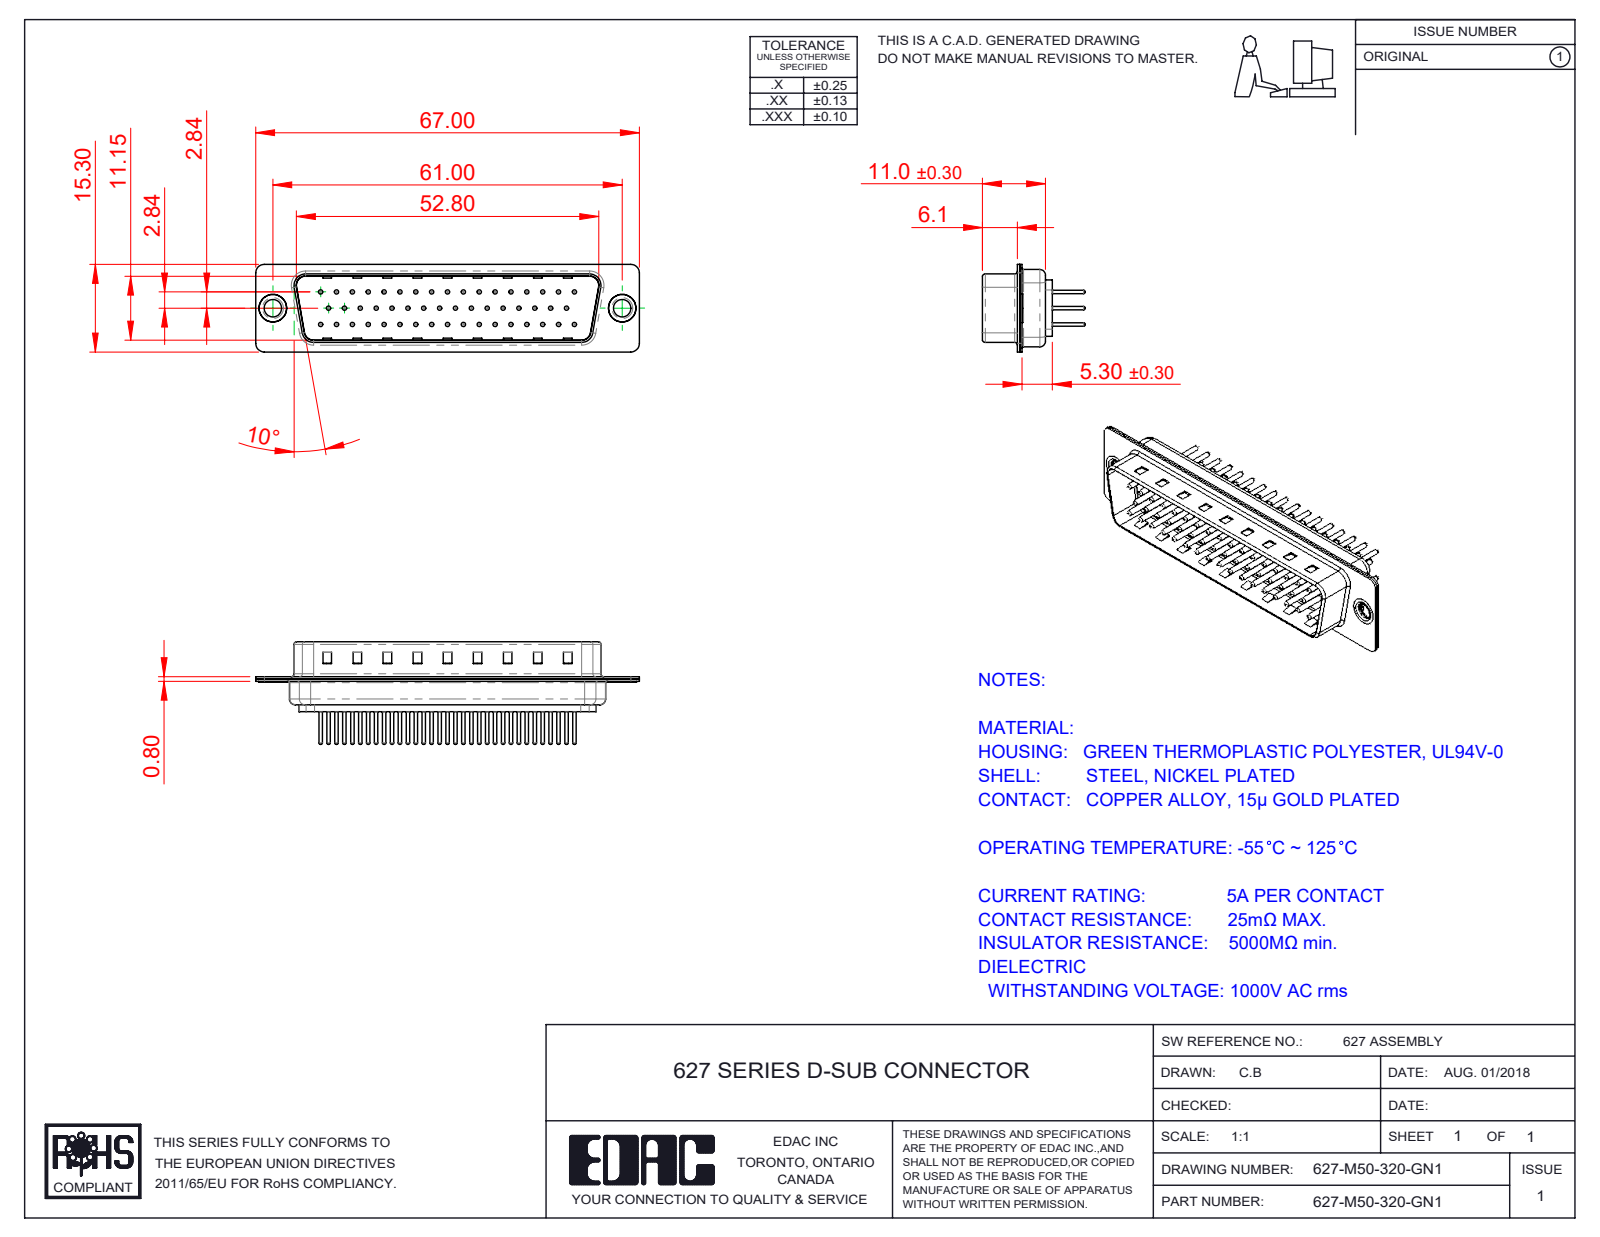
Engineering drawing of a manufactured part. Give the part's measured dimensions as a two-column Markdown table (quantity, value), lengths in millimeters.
| quantity | value |
| --- | --- |
| part name | 627M Housing_50 Contacts; 627M Contact Row 1_20; 627M Shell Rear_50 Contacts; 627M Thru Hole Rivet (+4 more) |
| STEP written by | SolidWorks 2020 (CONFIG_CONTROL_DESIGN) |
| units | millimeters |
| bodies | 55 solids, 2236 faces (553 planar, 825 cylindrical, 858 other) |
| overall size | 67 × 17.9 × 15.3 |
| volume | 4 447 mm³ |
| surface area | 10 554 mm² |
| round holes (diameter × count) | 0.75 × 50, 1.6 × 50, 2 × 50, 3.05 × 2, 4 × 2, 4.8 × 2 |
| round bosses / shafts (diameter × count) | 1.5 × 50, 0.6 × 50, 5 × 2, 4.9 × 2, 3.55 × 2 |
| partial cylindrical surfaces (radius × count) | 1.5 × 16, 2 × 12, 0.5 × 8, 1.6 × 8, 0.25 × 4, 0.6 × 4, 0.65 × 4, 0.9 × 4 |
| main face-to-face distances | 0.4, 11.55, 5.7, 6.1, 0.78, 0.77, 12.33, 12.32, 13.1, 5.3 |
| hole center spacings | 3.16, 2.77, 5.54, 8.31, 11.08, 13.85, 16.62, 5.03 |
